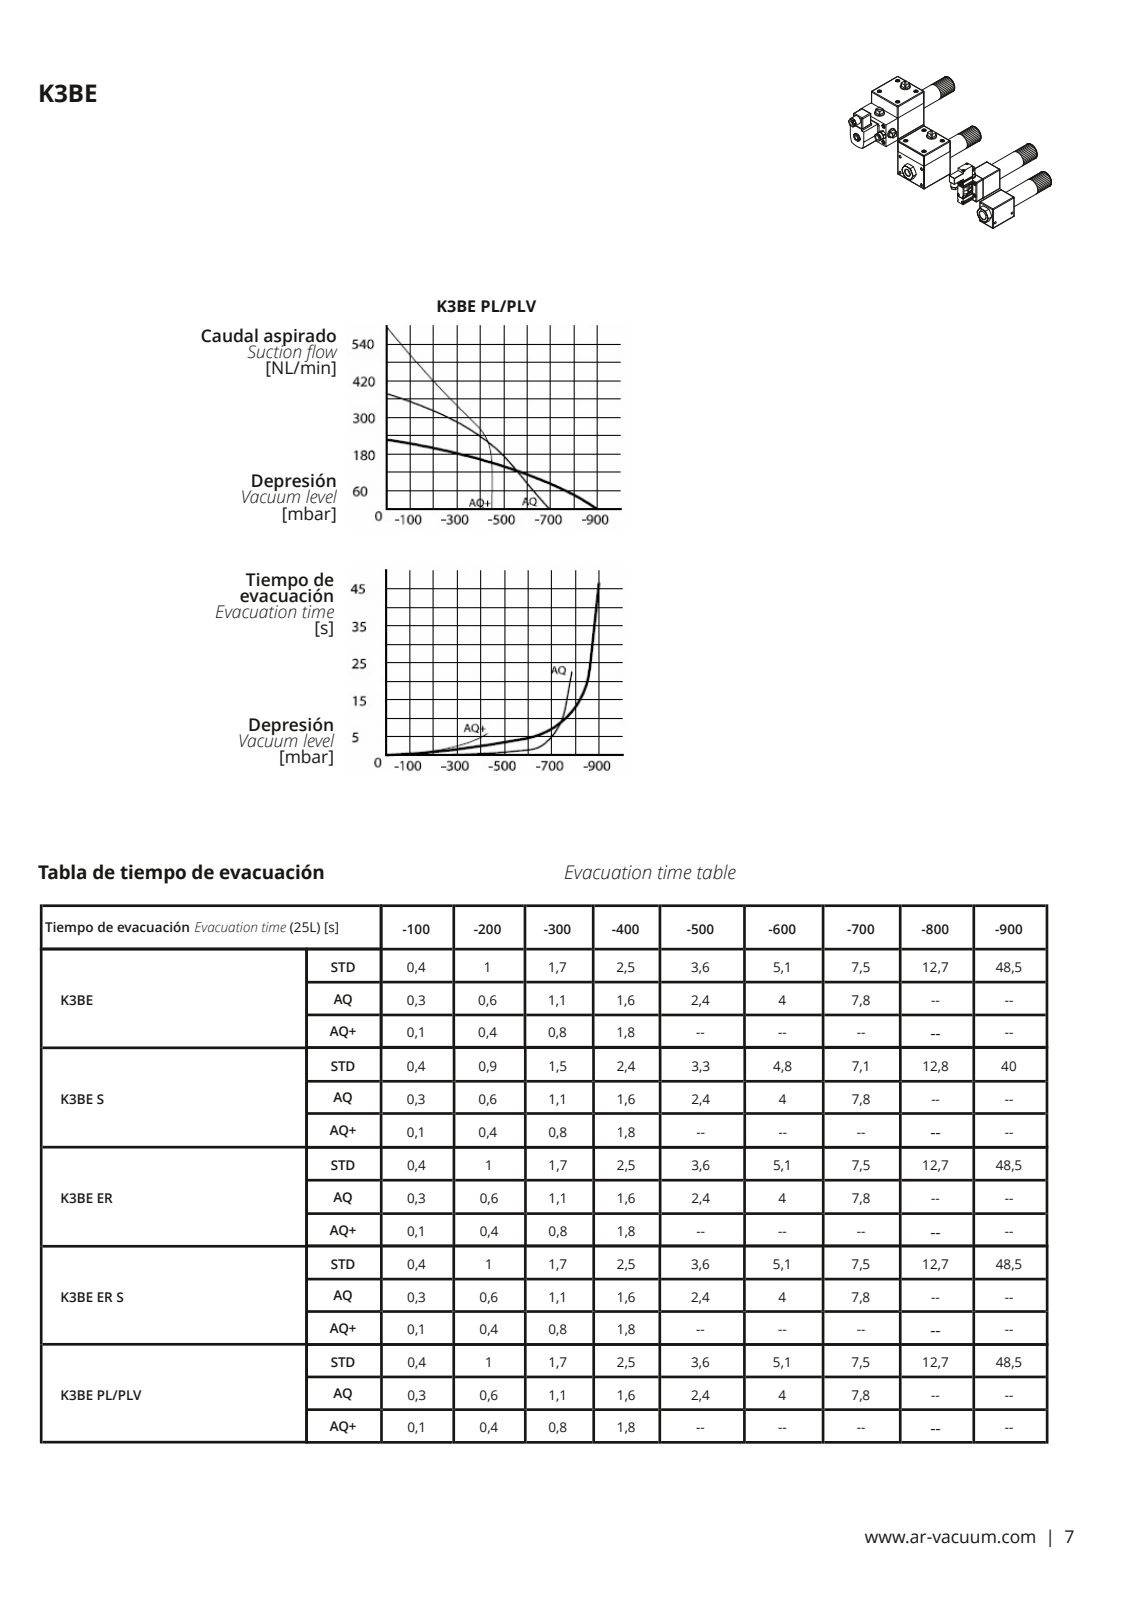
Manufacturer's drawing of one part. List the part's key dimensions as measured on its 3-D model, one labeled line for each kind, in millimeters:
Part name (STEP PRODUCT): Pieza10
STEP written by: Autodesk Inventor 2019 (AUTOMOTIVE_DESIGN)
Units: millimetres
Bodies: 1 solid, 118 faces (57 planar, 29 cylindrical, 32 other)
Overall size (bounding box): 188.5 × 50 × 40
Volume: 196 079 mm³ · Surface area: 41 502 mm²
Round holes (diameter × count): ⌀4.92 ×4, ⌀5.25 ×2, ⌀9 ×2, ⌀24.12 ×2, ⌀17 ×1, ⌀19 ×1
Round bosses / shafts (diameter × count): ⌀35 ×1, ⌀32 ×1, ⌀24 ×1
Partial cylindrical surfaces — rounded edges, fillets, slot ends (radius × count): R1.5 ×12
Main face-to-face distances: 40, 50, 64, 34.8, 15, 177.5, 113.5, 34.83, 11, 13
Hole centre spacings: 27.19, 29, 34.22, 54, 61.29, 50
